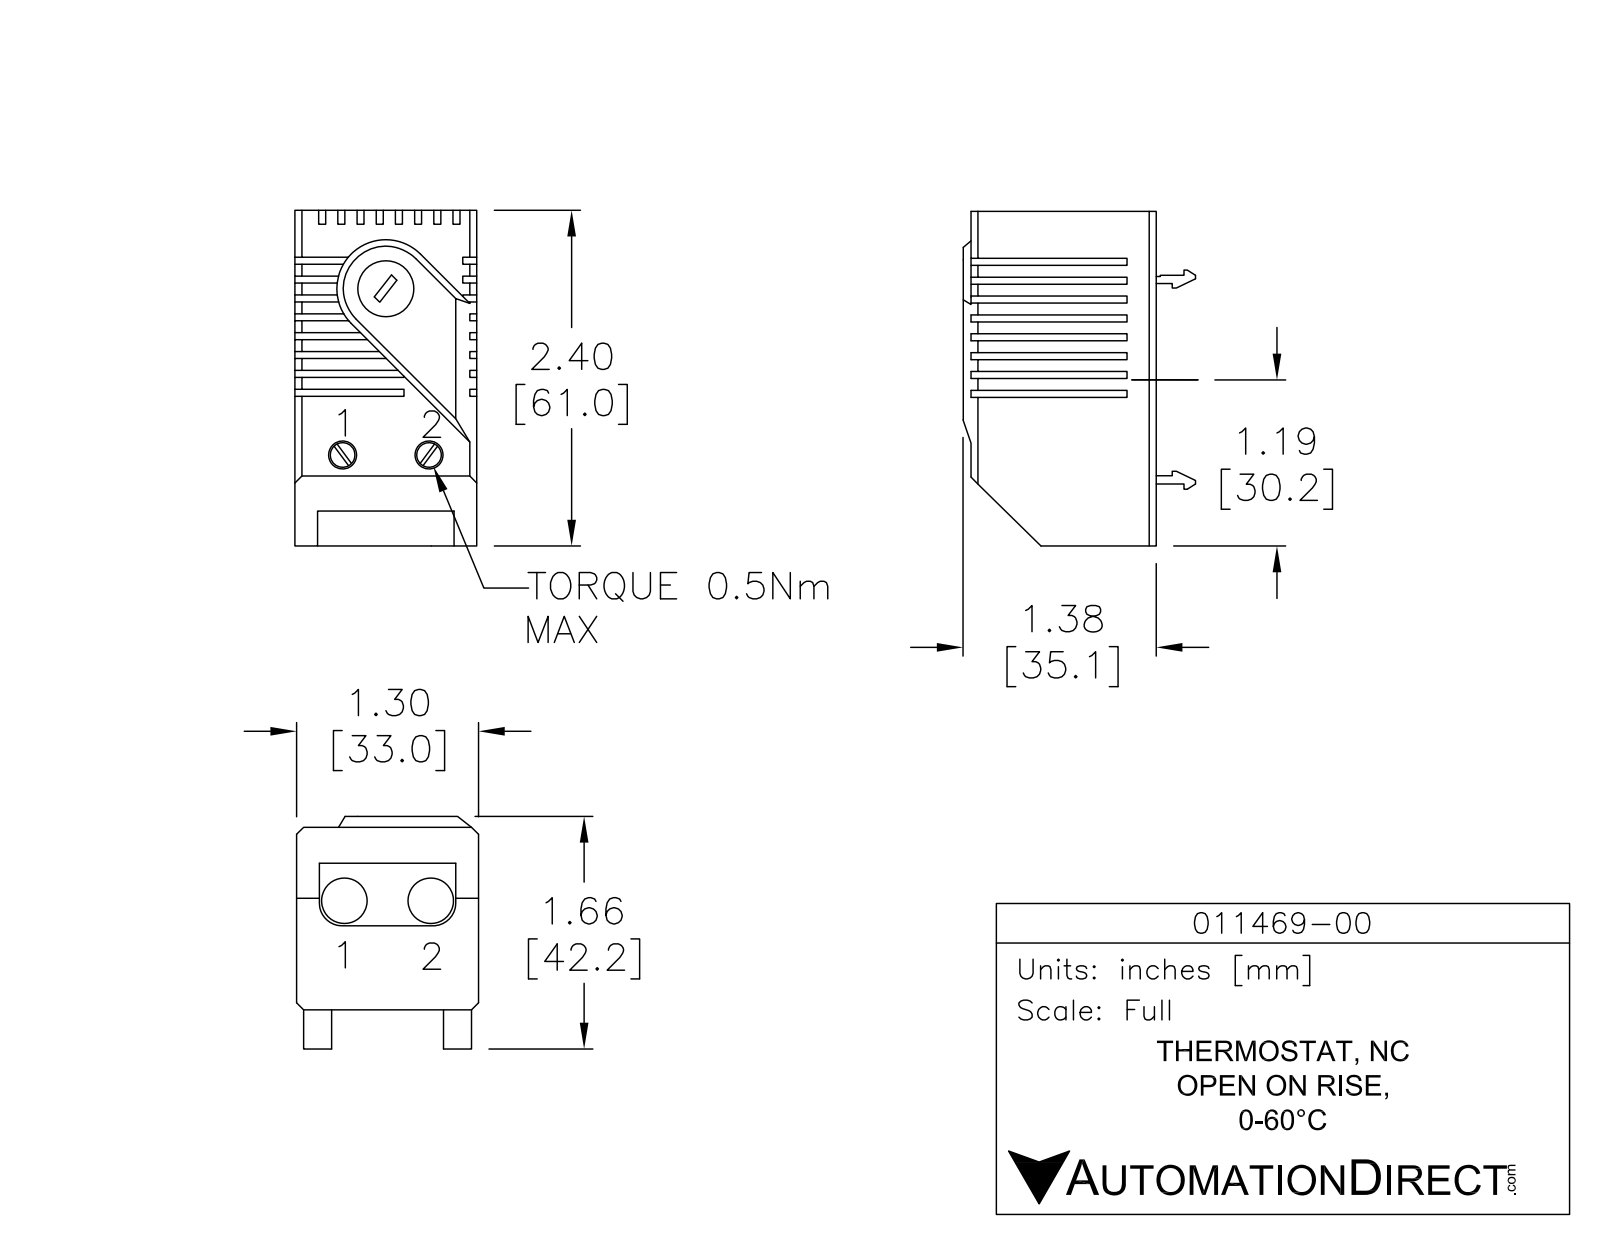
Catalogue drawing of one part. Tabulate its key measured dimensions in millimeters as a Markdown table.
| quantity | value |
| --- | --- |
| part name | 011469-00 |
| STEP written by | SolidWorks 2013 (AUTOMOTIVE_DESIGN) |
| units | millimeters |
| bodies | 1 solid, 424 faces (392 planar, 18 cylindrical, 14 other) |
| overall size | 59.9 × 42.4 × 33.1 |
| volume | 58 420 mm³ |
| surface area | 18 650 mm² |
| round holes (diameter × count) | 3 × 2, 6.2 × 2 |
| round bosses / shafts (diameter × count) | 9.7 × 1, 7.6 × 1, 7.5 × 1 |
| partial cylindrical surfaces (radius × count) | 14 × 2, 3.8 × 1 |
| main face-to-face distances | 4.6, 2.3, 6.9, 11.4, 1.3, 9.1, 10.2, 1, 3.3, 2.3 |
| hole center spacings | 10.4 |
